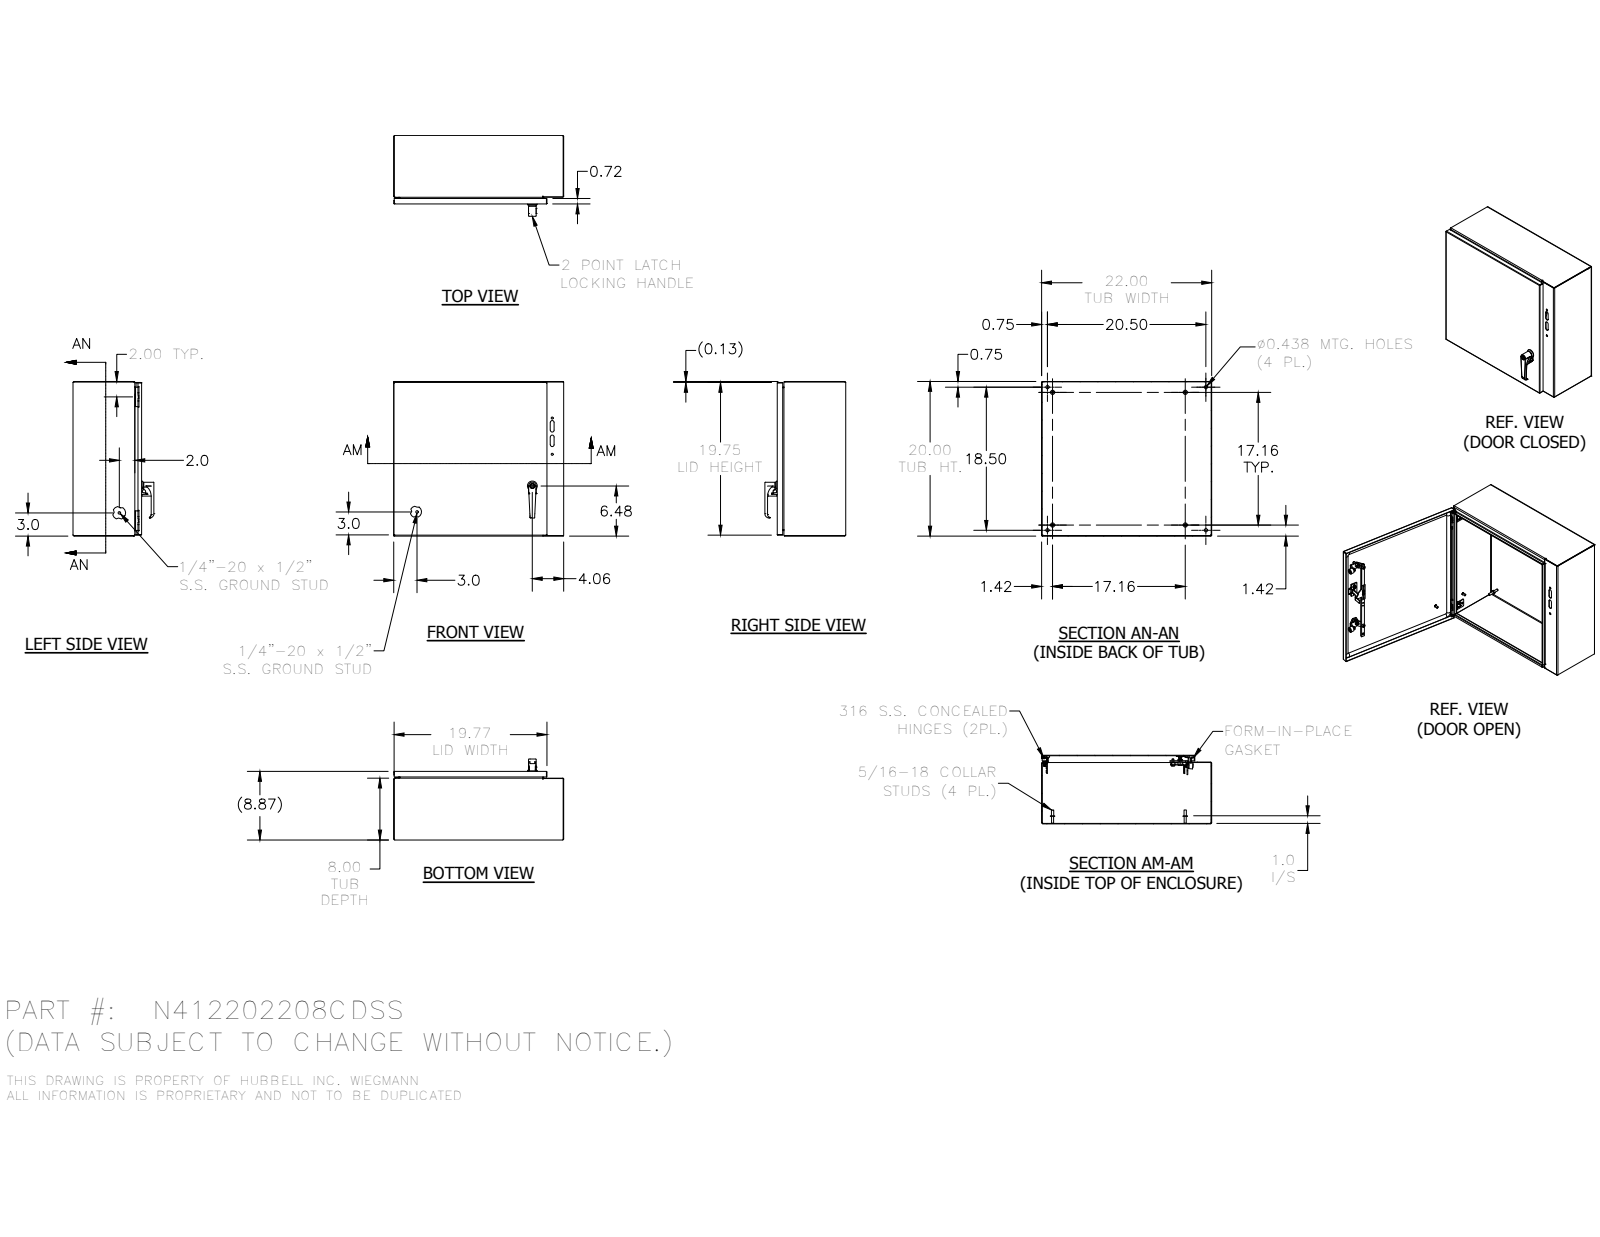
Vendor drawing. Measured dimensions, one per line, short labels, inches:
name: N412202208CD
written by: SolidWorks 2019 (AUTOMOTIVE_DESIGN)
unit: in
bodies: 60 solids, 2068 faces (810 planar, 741 cylindrical, 517 other)
size: 22 × 20 × 10.512
volume: 132.1 in³; area: 3 533 in²
holes: 4× ⌀0.093, 4× ⌀0.145, 4× ⌀0.152, 4× ⌀0.156, 4× ⌀0.167, 4× ⌀0.172, 4× ⌀0.187, 4× ⌀0.437, 3× ⌀0.32, 2× ⌀0.196, 2× ⌀0.211, 2× ⌀0.22
bosses: 12× ⌀0.25, 8× ⌀0.3, 4× ⌀0.563, 4× ⌀0.437, 4× ⌀0.36, 4× ⌀0.32, 4× ⌀0.275, 4× ⌀0.256
rounds: 38× R0.02, 31× R0.012, 26× R0.05, 25× R0.125, 18× R0.016, 16× R0.016, 16× R0.025, 16× R0.09
face distances: 0.074, 8.843, 8.769, 8.917, 19.926, 21.926, 7.926, 0.917, 20, 19.852
hole spacings: 16, 0.5, 10.9, 20.87, 0.656, 0.66, 0.984, 1.307
